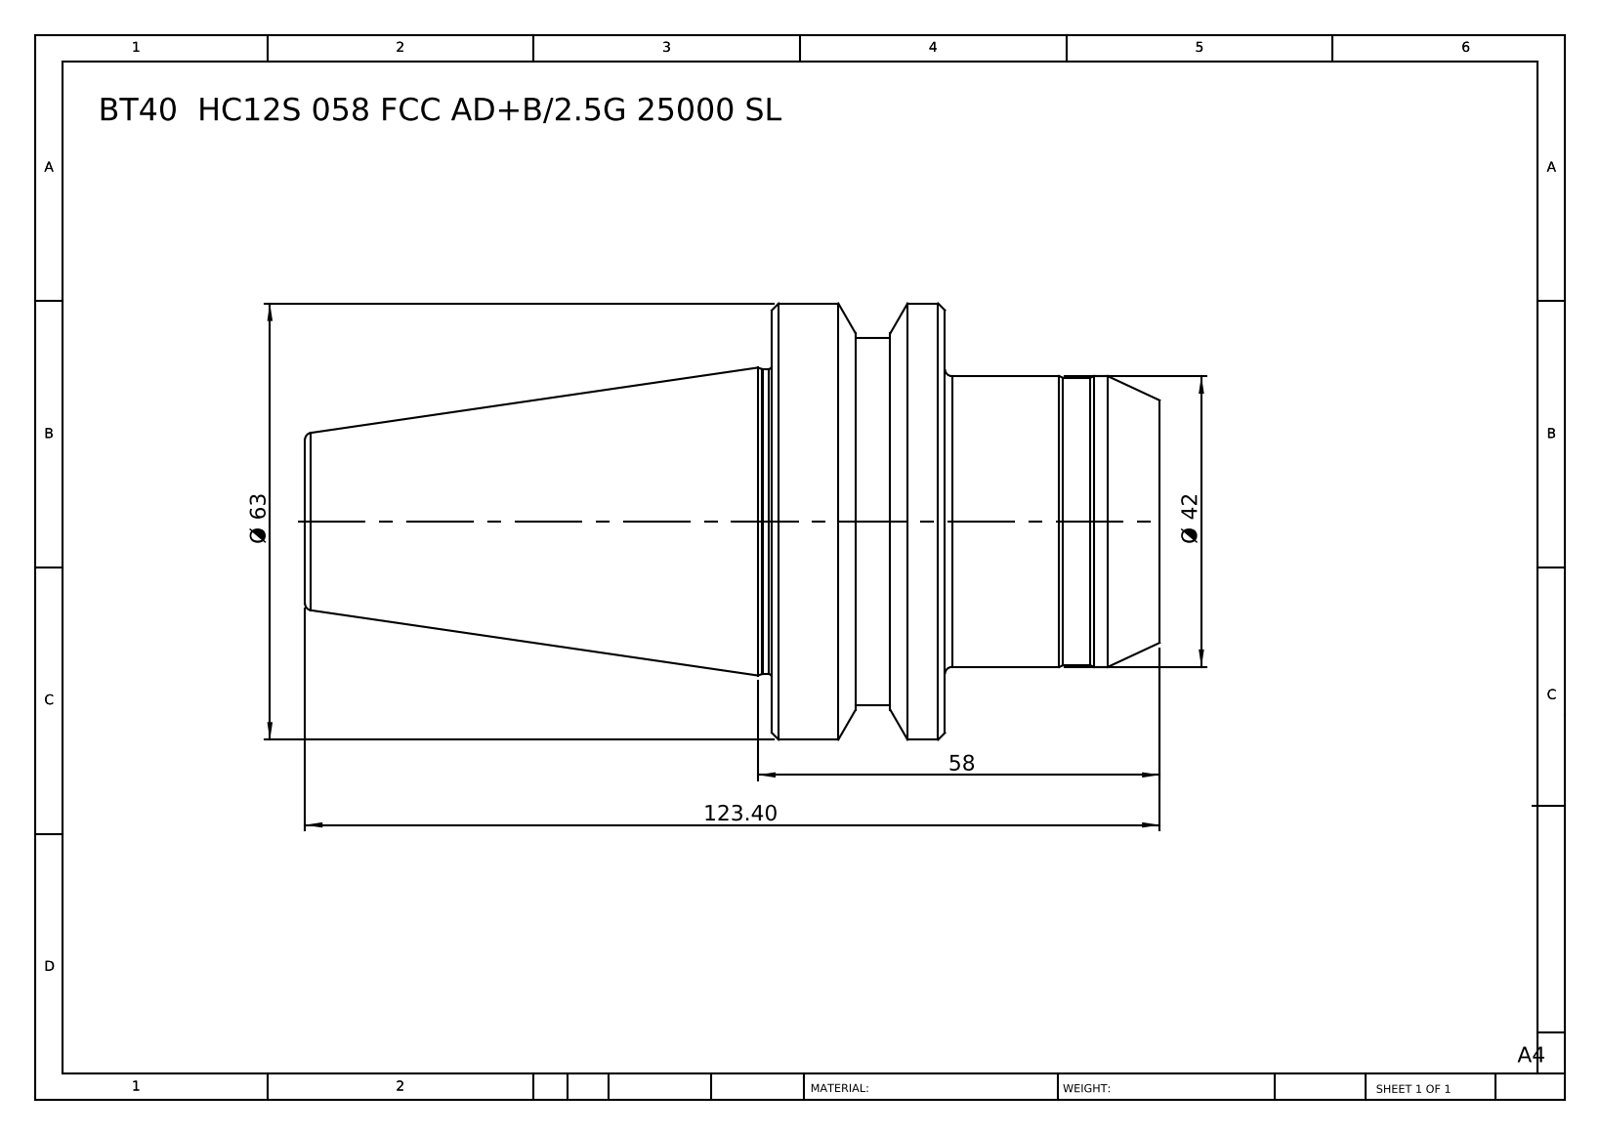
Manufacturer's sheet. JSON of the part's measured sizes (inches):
{"part_name": "BT40 HC12S 058 FCC AD+B-2.5G 25000 SL", "step_written_by": "SolidWorks 2014 (CONFIG_CONTROL_DESIGN)", "units": "inches", "bodies": {"solids": 1, "faces": 46, "planar": 6, "cylindrical": 14, "other": 26}, "overall_size": [4.858, 2.48, 2.48], "volume_in3": 10.96, "surface_area_in2": 34.04, "round_bosses_or_shafts": [[2.48, 1], [2.087, 1], [1.732, 1], [1.654, 1], [1.634, 1]], "face_to_face_distances": [0.984, 1.22, 2.205, 4.858, 3.638, 2.654, 1.531, 0.311, 0.673, 3.327]}
